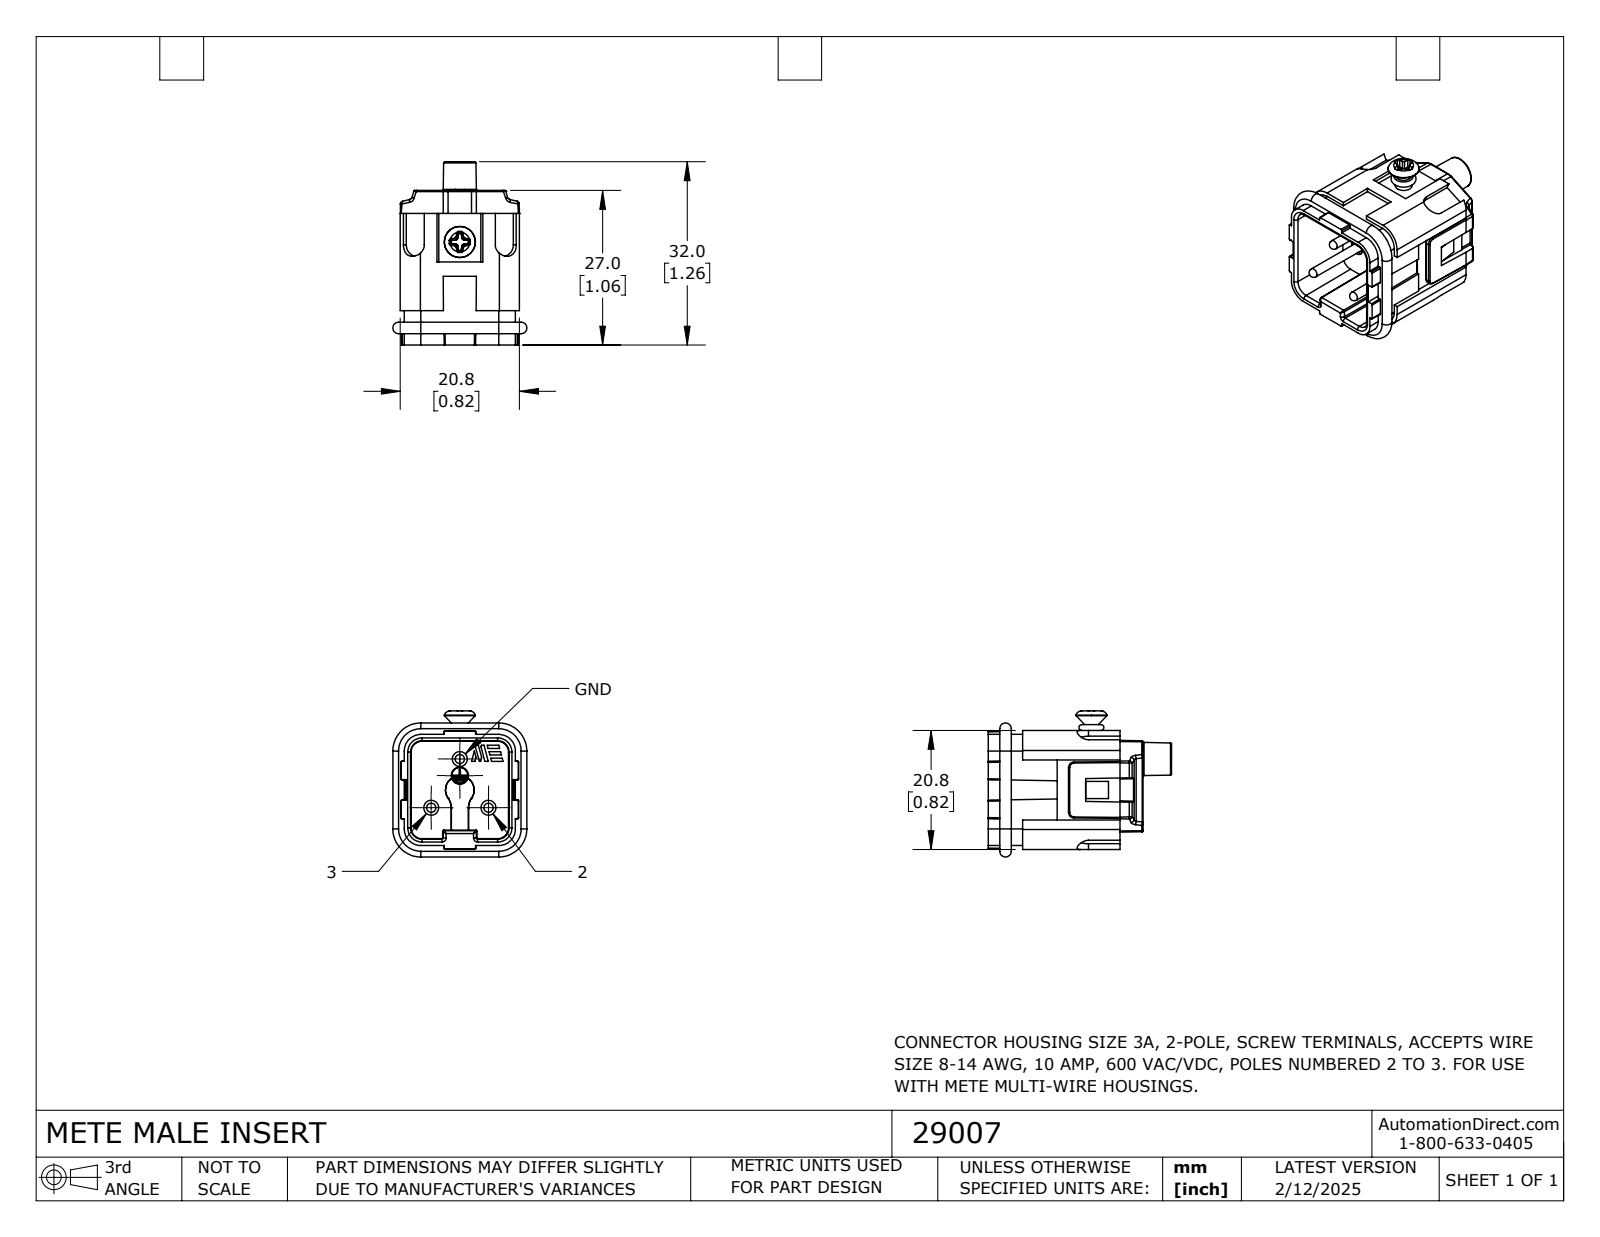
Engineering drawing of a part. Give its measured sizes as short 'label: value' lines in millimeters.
name: 29007
written by: SolidWorks 2024 (CONFIG_CONTROL_DESIGN)
unit: mm
bodies: 1 solid, 635 faces (283 planar, 182 cylindrical, 170 other)
size: 32 × 25.5 × 23.4
volume: 6 870 mm³; area: 5 171 mm²
holes: 3× ⌀2.6, 1× ⌀2.8, 1× ⌀3.1
bosses: 4× ⌀2.9, 3× ⌀2.4, 3× ⌀1.6, 1× ⌀3
rounds: 46× R0.2, 17× R0.5, 12× R0.1, 12× R0.3, 9× R2, 6× R1, 5× R2.9, 4× R0.4
face distances: 11.5, 0.7, 20.1, 4, 2, 1, 19, 20.8, 18.8, 23
hole spacings: 7.5, 9.9, 2.9, 10
